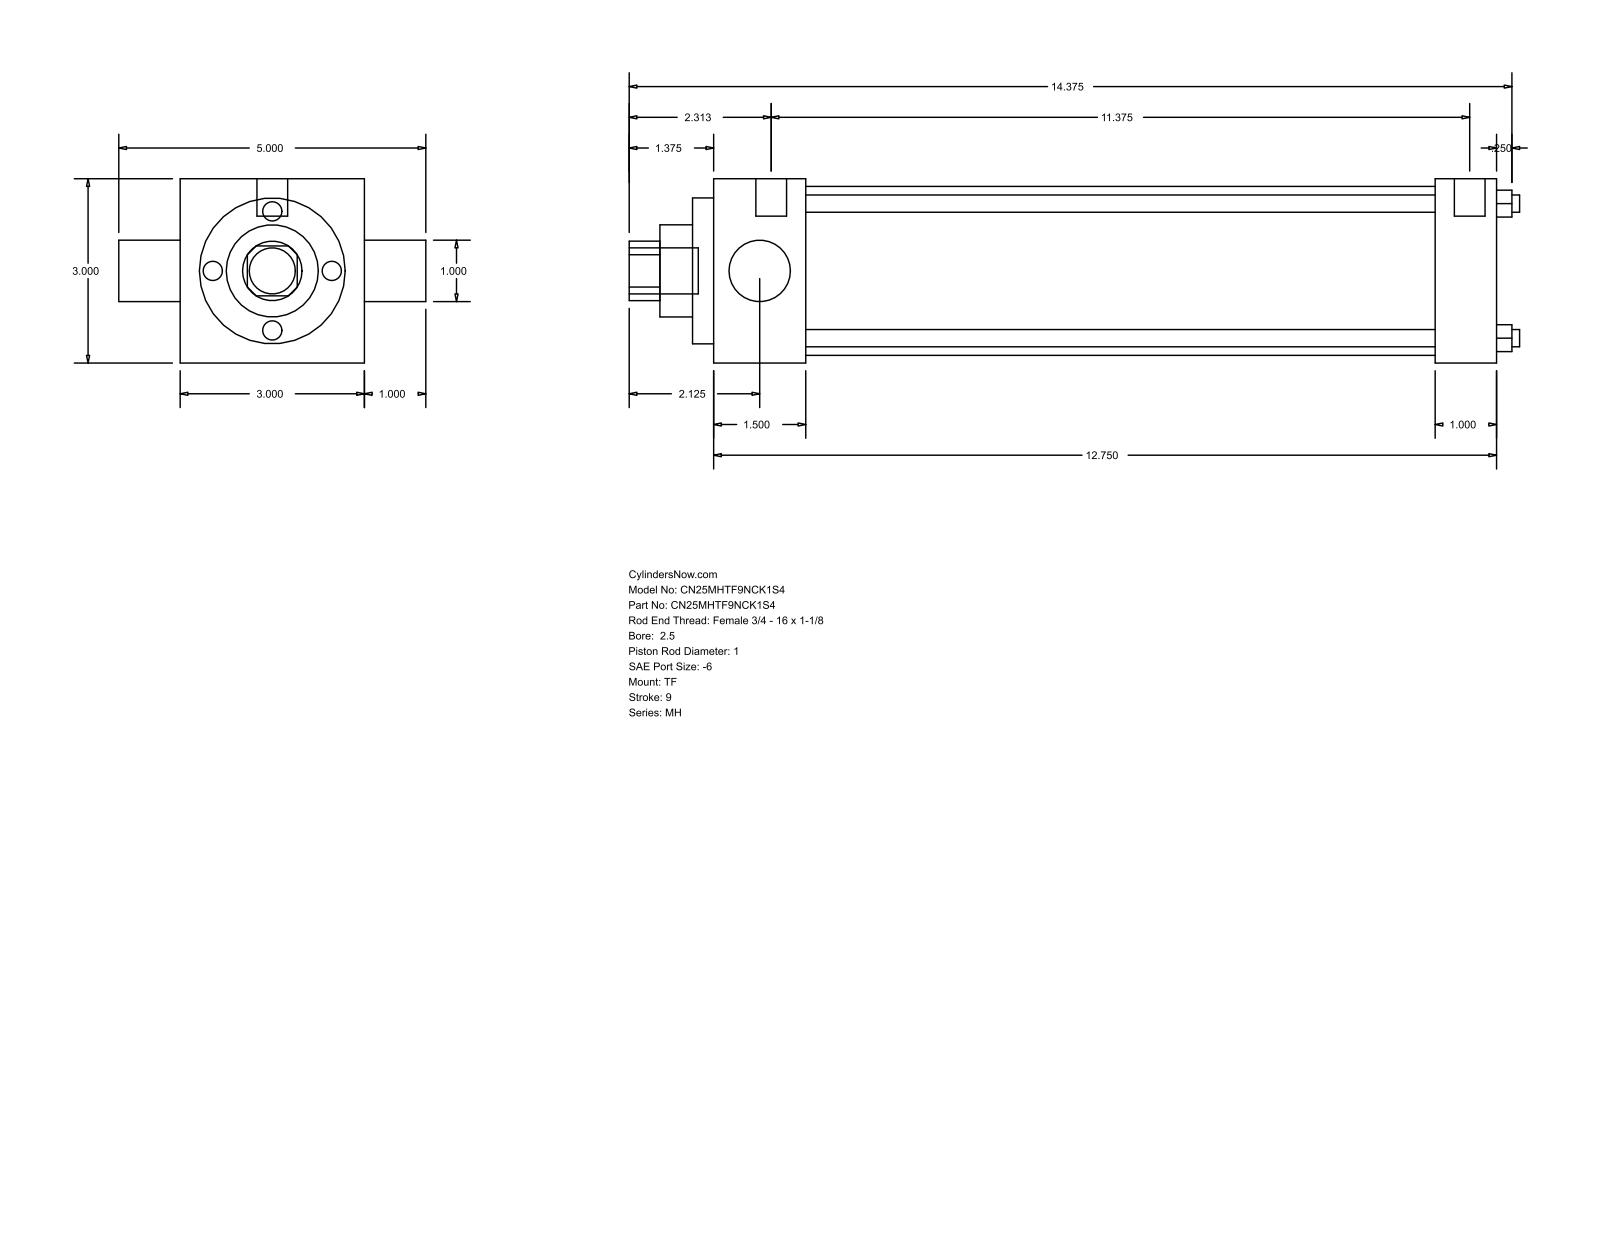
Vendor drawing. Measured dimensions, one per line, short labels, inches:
name: MH_TF__0250_1
written by: GSSL Pune (CONFIG_CONTROL_DESIGN)
unit: in
bodies: 0 solids, 86 faces (61 planar, 25 cylindrical, 0 other)
size: 14.5 × 5 × 3
holes: 4× ⌀0.281, 2× ⌀1, 1× ⌀1.5, 1× ⌀2.375, 1× ⌀2.75
bosses: 3× ⌀0.219, 2× ⌀0.5, 1× ⌀0.75
rounds: 1× R0.484
face distances: 3, 12.75, 1, 1.5, 11.25, 11.75, 10.25, 0.344, 1.844, 12.094
hole spacings: 1.548, 2.19, 3.097
